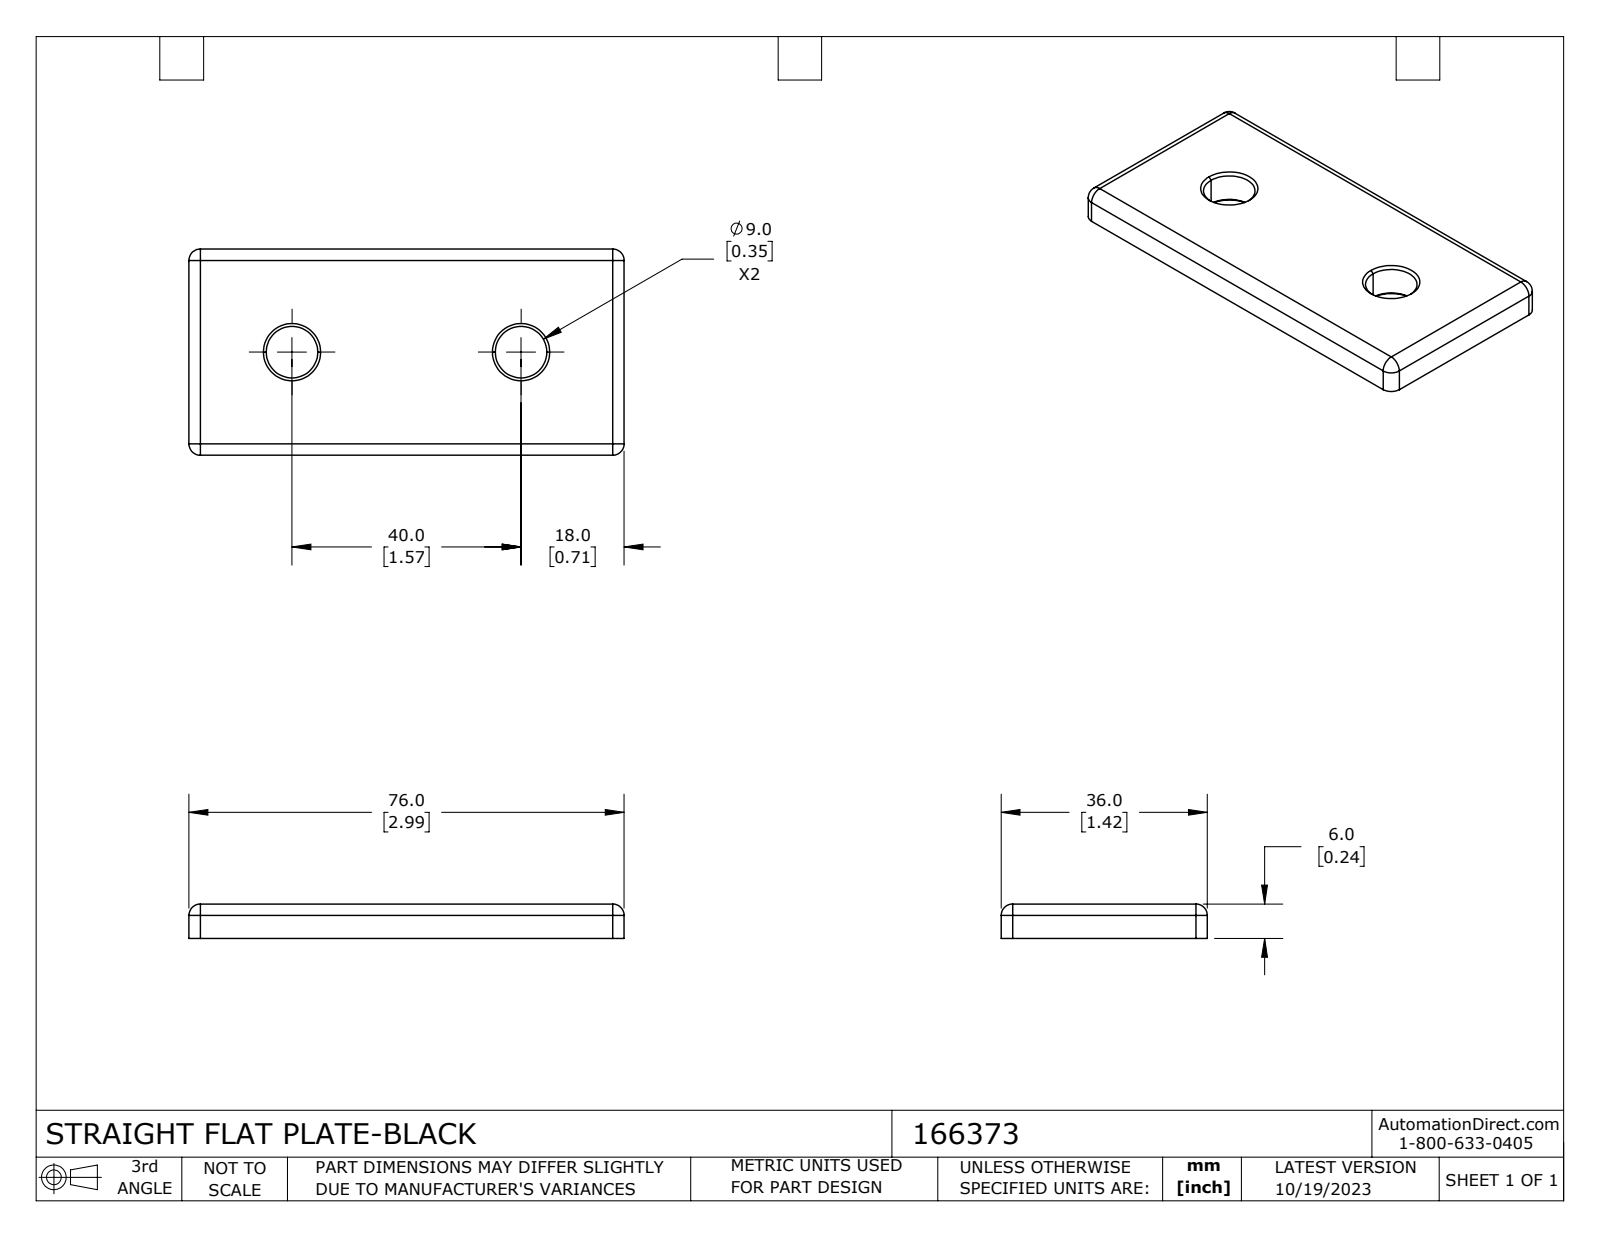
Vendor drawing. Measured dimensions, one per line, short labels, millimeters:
name: 166373
written by: SolidWorks 2023 (CONFIG_CONTROL_DESIGN)
unit: mm
bodies: 1 solid, 30 faces (6 planar, 12 cylindrical, 12 other)
size: 76 × 36 × 6
volume: 15 430 mm³; area: 6 650 mm²
holes: 2× ⌀9
rounds: 8× R2
face distances: 6, 36, 76
hole spacings: 40
